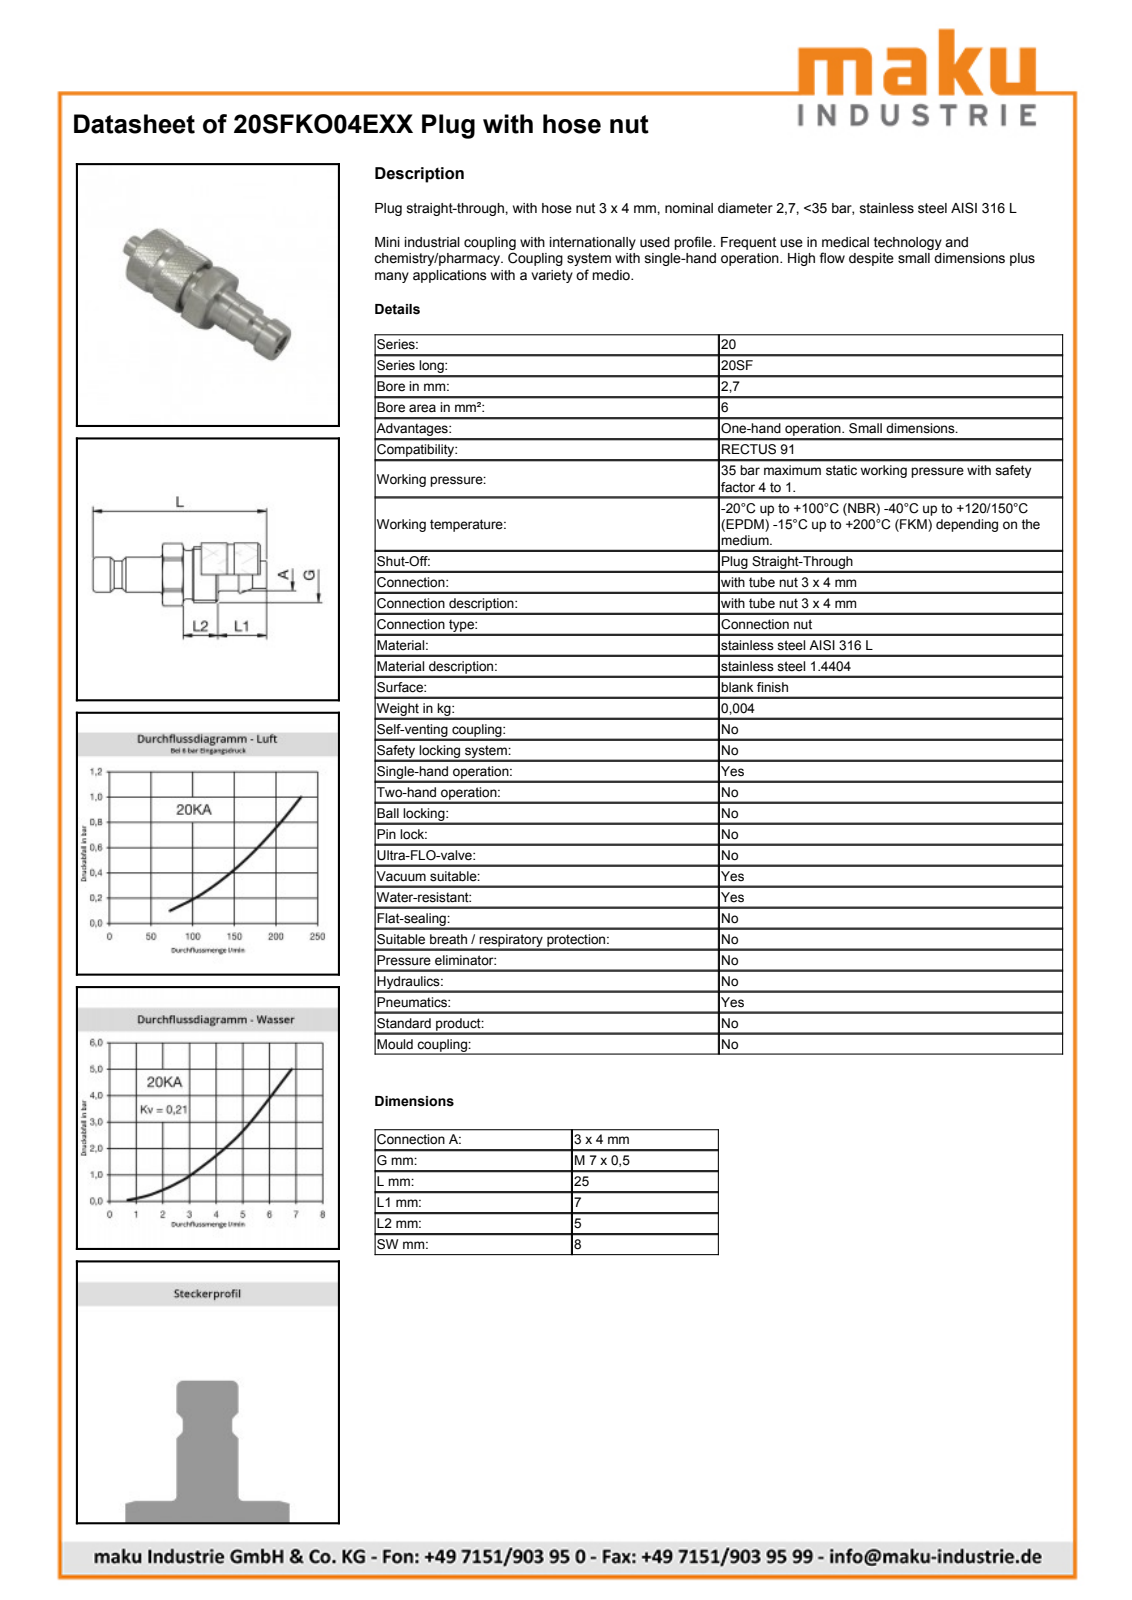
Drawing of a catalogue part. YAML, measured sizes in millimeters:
part_name: "D108492; D108481; D106063"
step_written_by: "Autodesk Inventor 2013 (AUTOMOTIVE_DESIGN)"
units: millimeters
bodies: {solids: 2, faces: 67, planar: 16, cylindrical: 20, other: 31}
overall_size: [25, 9, 8.1]
volume: 661
surface_area: 1146
round_holes:
  - {diameter: 1.95, count: 1}
  - {diameter: 2.7, count: 1}
  - {diameter: 4.25, count: 1}
  - {diameter: 6.5, count: 1}
round_bosses_or_shafts:
  - {diameter: 8.1, count: 1}
  - {diameter: 7.7, count: 1}
  - {diameter: 7, count: 1}
  - {diameter: 6, count: 1}
  - {diameter: 5, count: 1}
  - {diameter: 3.95, count: 1}
  - {diameter: 3.5, count: 1}
  - {diameter: 2.85, count: 1}
partial_cylinders:
  - {radius: 4.5, count: 1}
face_to_face_distances: [8, 13.87, 5.87, 8.5, 2.63, 5.37, 10.87, 5, 2.37, 3]
